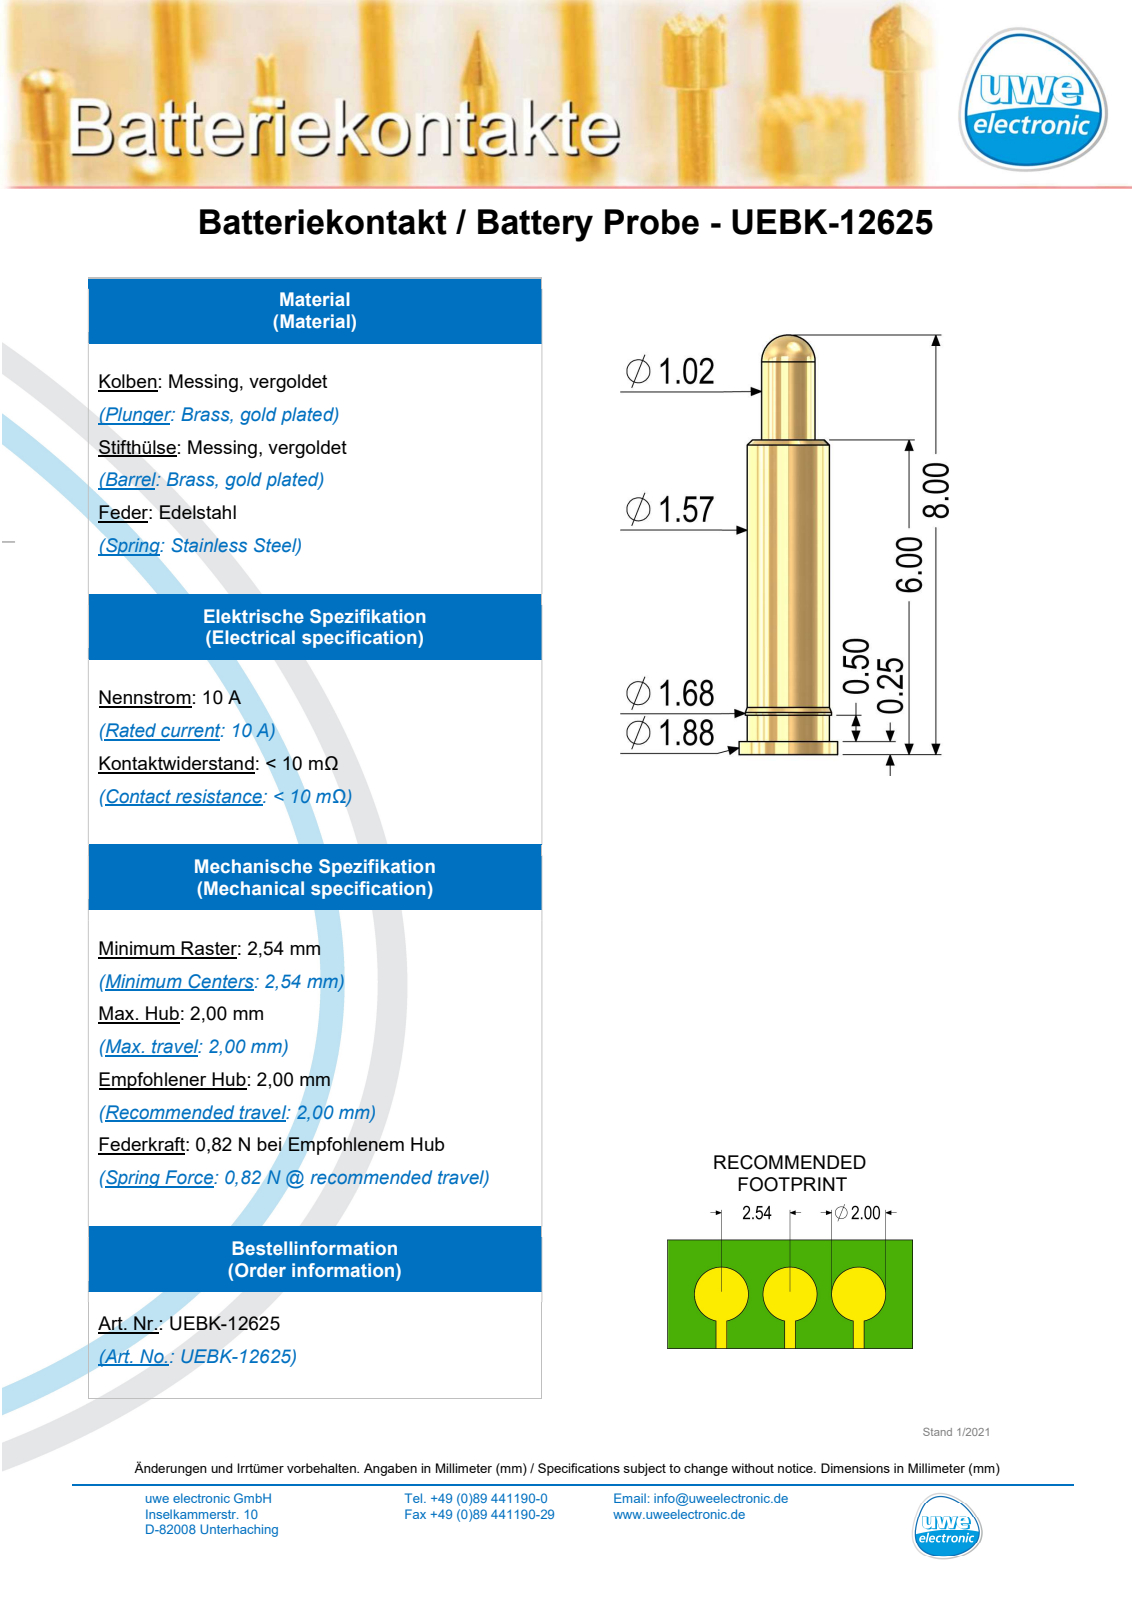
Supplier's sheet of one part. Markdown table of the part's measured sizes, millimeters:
| quantity | value |
| --- | --- |
| part name | UEBK-12625 |
| STEP written by | SolidWorks 2015 (AUTOMOTIVE_DESIGN) |
| units | millimeters |
| bodies | 1 solid, 20 faces (4 planar, 8 cylindrical, 8 other) |
| overall size | 8 × 1.88 × 1.88 |
| volume | 13 mm³ |
| surface area | 41 mm² |
| round bosses / shafts (diameter × count) | 1.88 × 1, 1.57 × 1, 1.02 × 1 |
| main face-to-face distances | 6, 5.75, 0.75, 0.5, 5.25 |
